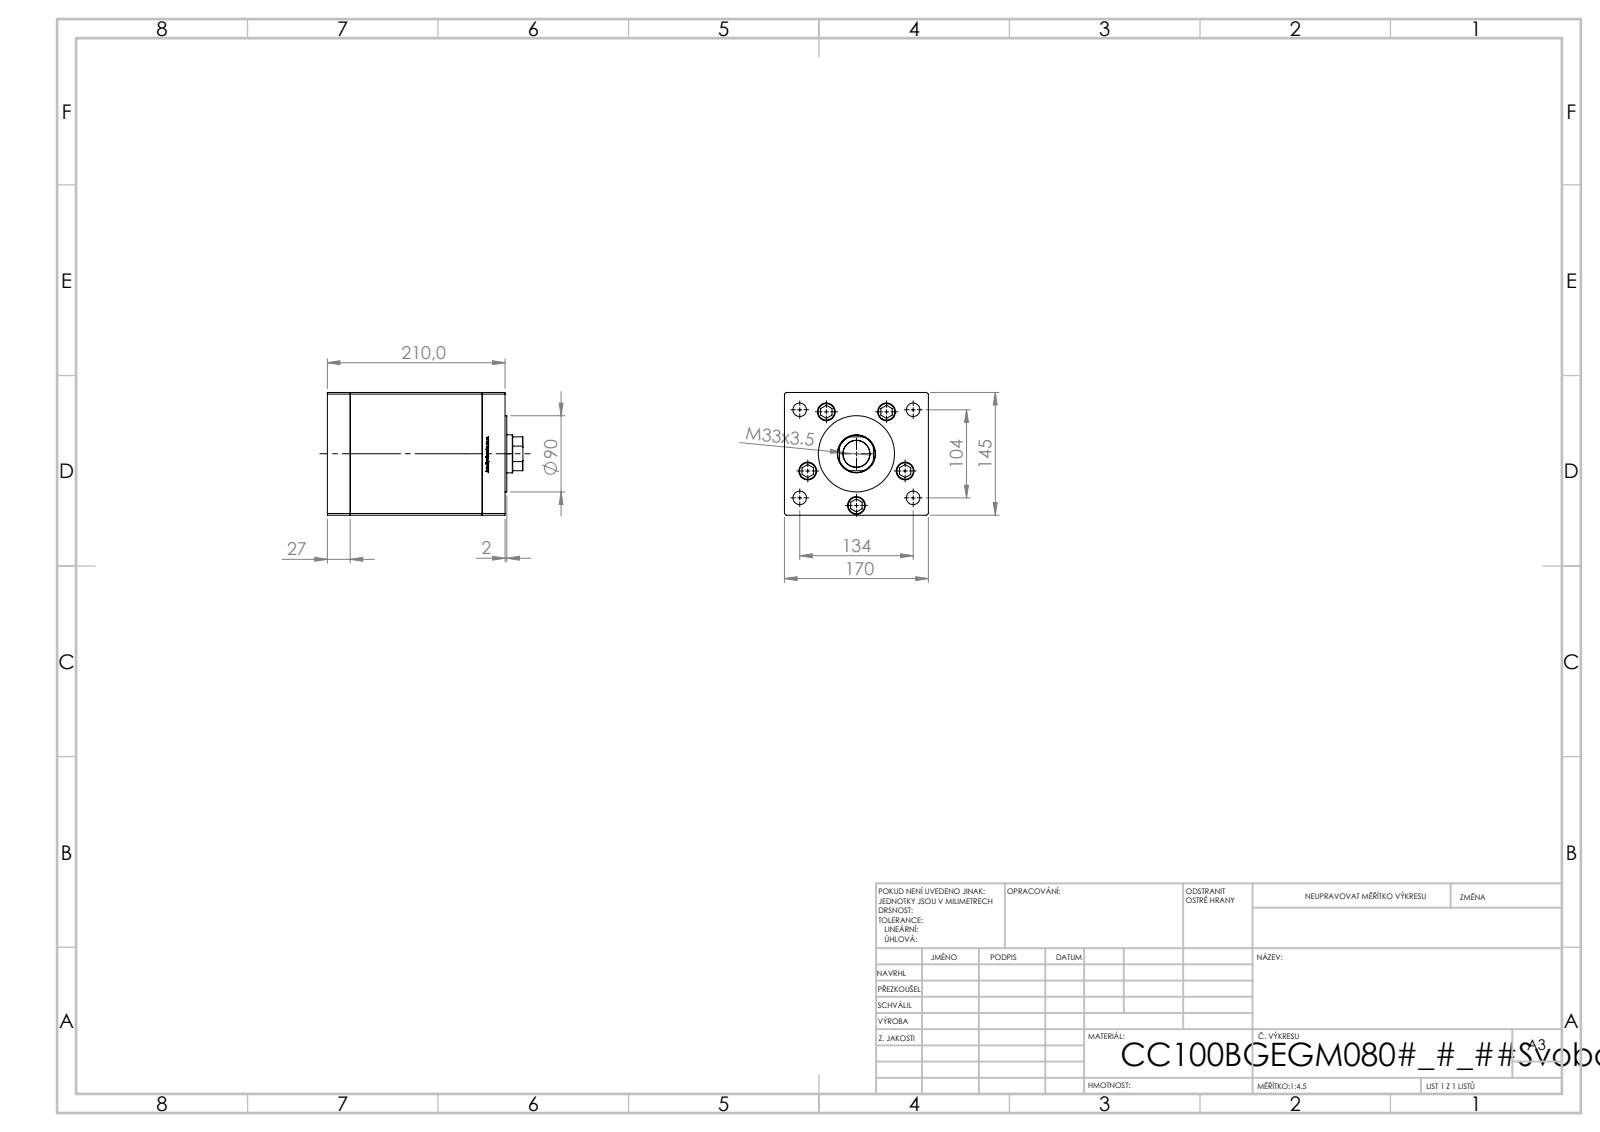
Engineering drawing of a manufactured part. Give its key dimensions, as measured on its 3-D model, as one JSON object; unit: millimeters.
{"part_name": "V220C_VC_B; V220C_FRONT_B; V220C BACK_B; V220C_B MIDDLE (+1 more)", "step_written_by": "SolidWorks 2019 (CONFIG_CONTROL_DESIGN)", "units": "millimeters", "bodies": {"solids": 14, "faces": 1185, "planar": 464, "cylindrical": 147, "other": 574}, "overall_size": [231, 170, 145], "volume_mm3": 4515000, "surface_area_mm2": 433039, "round_holes": [[17.5, 5], [21, 5], [16, 4], [2, 2], [13.16, 2], [31.5, 1], [45, 1]], "round_bosses_or_shafts": [[8, 5], [100, 1], [90, 1]], "partial_cylinders_radius": [[0.93, 2], [22, 1]], "face_to_face_distances": [145, 27, 183, 156, 170, 38, 11, 210, 172, 174], "hole_center_spacings": [61, 84.81, 31.53, 33.06, 67.6, 70.44, 72.95, 73.26]}
